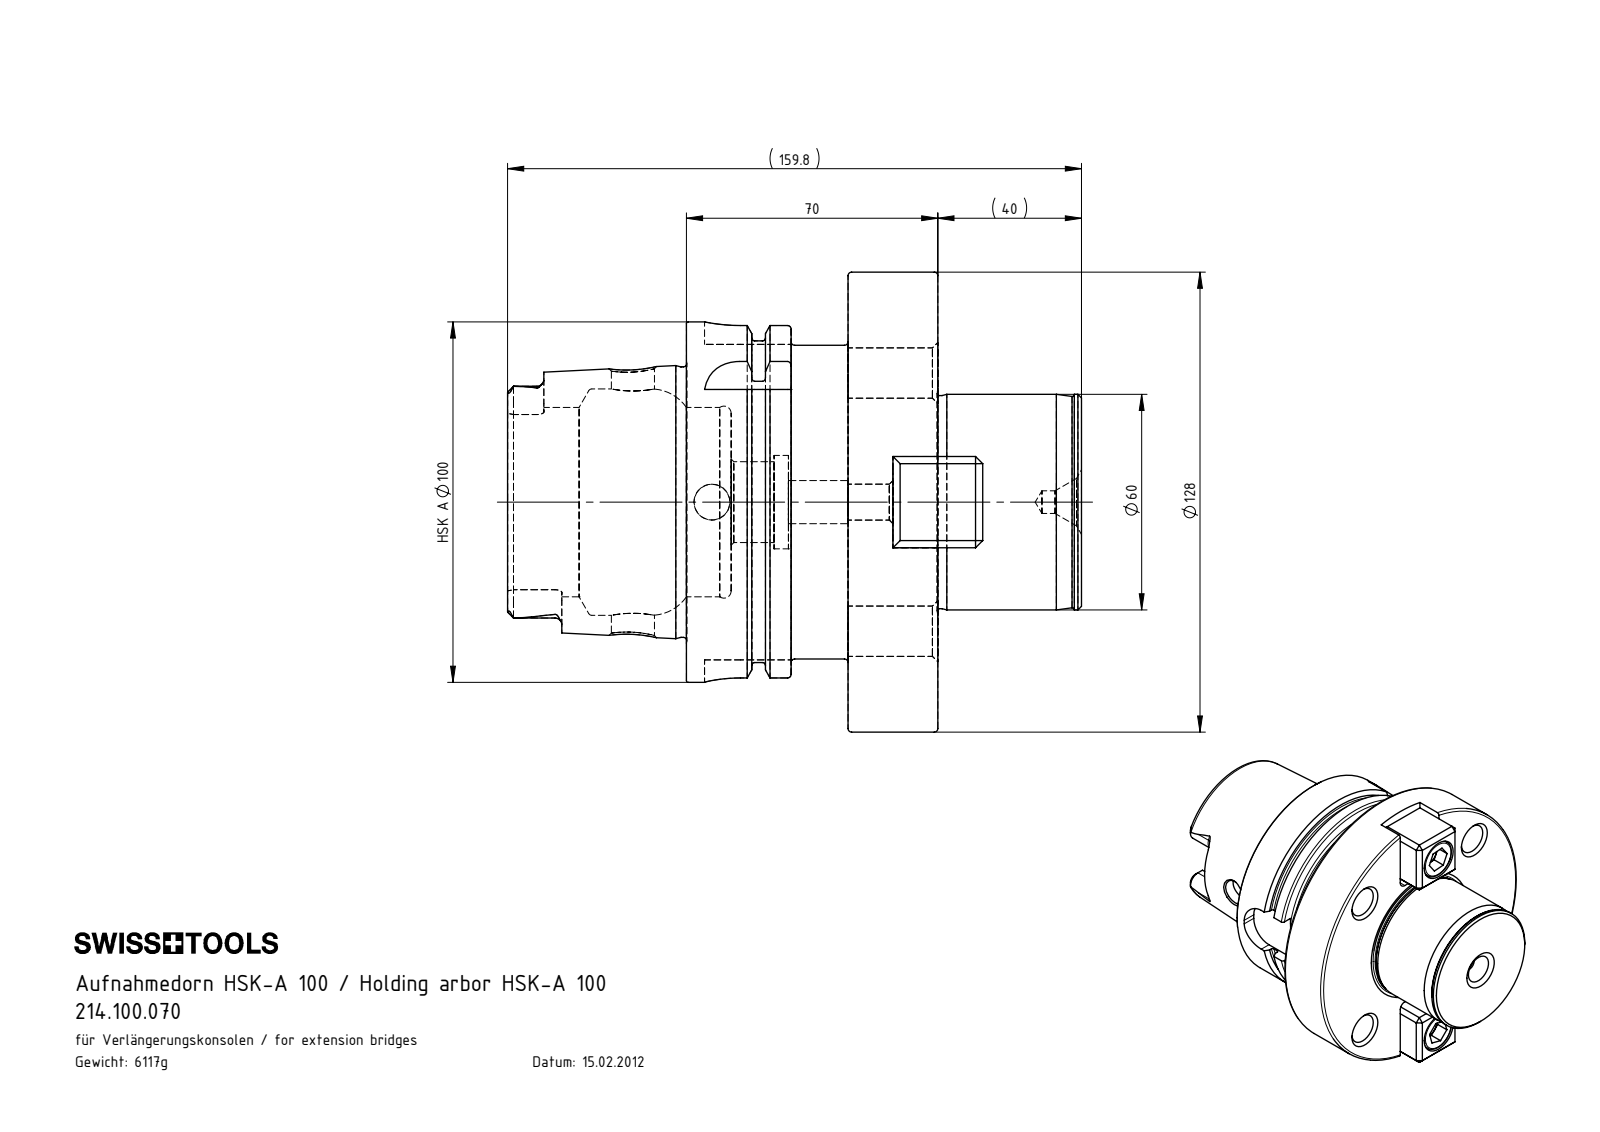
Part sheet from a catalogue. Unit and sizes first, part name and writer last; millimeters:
Units: millimetres
Overall size (bounding box): 159.8 × 128 × 128
Round holes (diameter × count): ⌀14 ×4, ⌀10 ×3, ⌀12 ×2, ⌀13 ×2, ⌀19 ×2, ⌀6.3 ×1, ⌀22.5 ×1, ⌀26 ×1, ⌀52.7 ×1, ⌀63 ×1
Round bosses / shafts (diameter × count): ⌀18 ×2, ⌀12 ×2, ⌀128 ×1, ⌀100.3 ×1, ⌀91.95 ×1, ⌀87.3 ×1, ⌀75.26 ×1, ⌀60 ×1
Partial cylindrical surfaces — rounded edges, fillets, slot ends (radius × count): R1.9 ×8, R3 ×4, R4.88 ×4, R10 ×4
Main face-to-face distances: 25, 12.5, 45, 70, 25.4, 110, 65, 40, 57.5, 52.5
Hole centre spacings: 38.23, 50.8, 71.84, 92.2, 49, 101.6, 98
Volume: 779 252 mm³ · Surface area: 104 489 mm²
Bodies: 5 solids, 346 faces (127 planar, 90 cylindrical, 129 other)
Part name (STEP PRODUCT): U00-D60.ER1.025; HA0-D60.K01.070; HA0-D60.K01.070_Weichbearbeitung; ISO 4762 - M12 x 25_PreviewCfg
STEP written by: SolidWorks 2017 (CONFIG_CONTROL_DESIGN)
